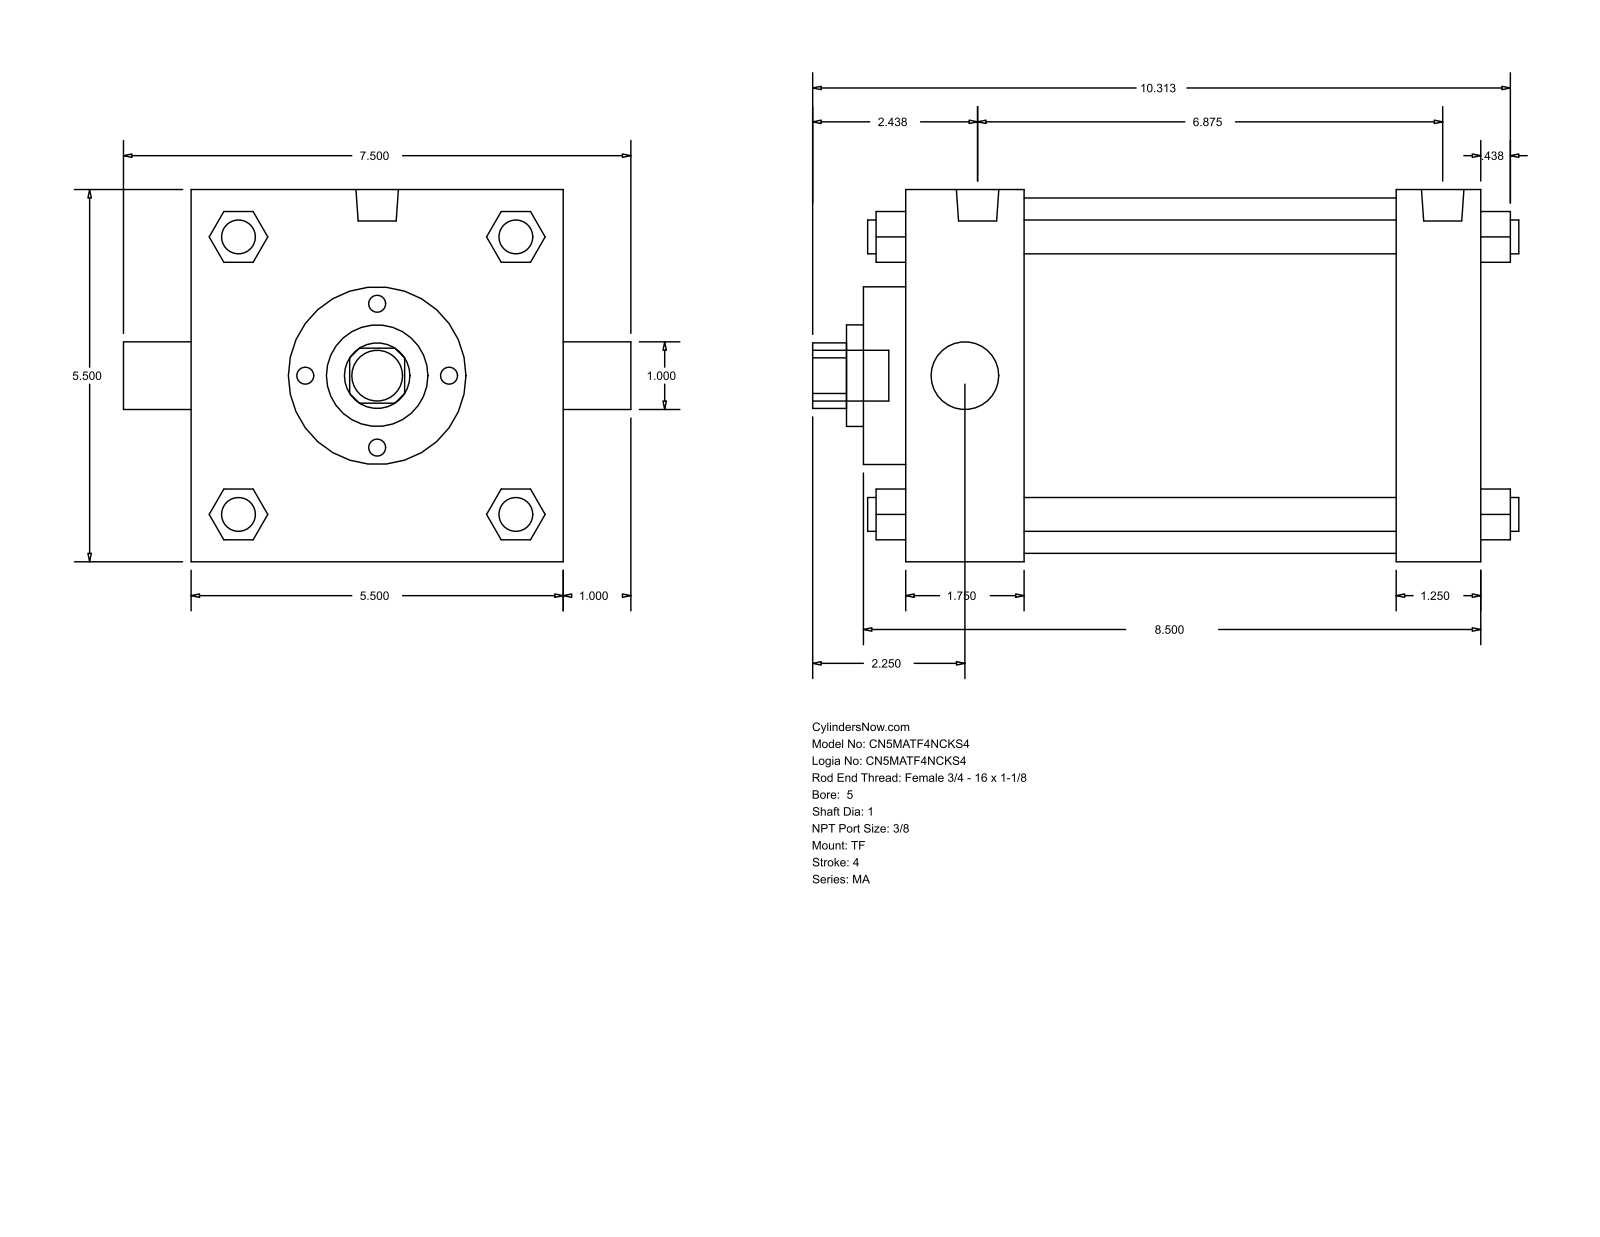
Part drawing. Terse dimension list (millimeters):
name: MA_TF__0500_1
written by: GSSL Pune (CONFIG_CONTROL_DESIGN)
unit: mm
bodies: 0 solids, 122 faces (93 planar, 29 cylindrical, 0 other)
size: 265.11 × 190.5 × 139.7
holes: 2× ⌀25.4, 1× ⌀38.1, 1× ⌀66.67, 1× ⌀133.35
bosses: 4× ⌀12.7, 3× ⌀11.11, 2× ⌀15.93, 1× ⌀19.05
rounds: 1× R12.29
face distances: 139.7, 215.9, 184.15, 31.75, 44.46, 139.69, 171.44, 15.87, 60.33, 200.02
